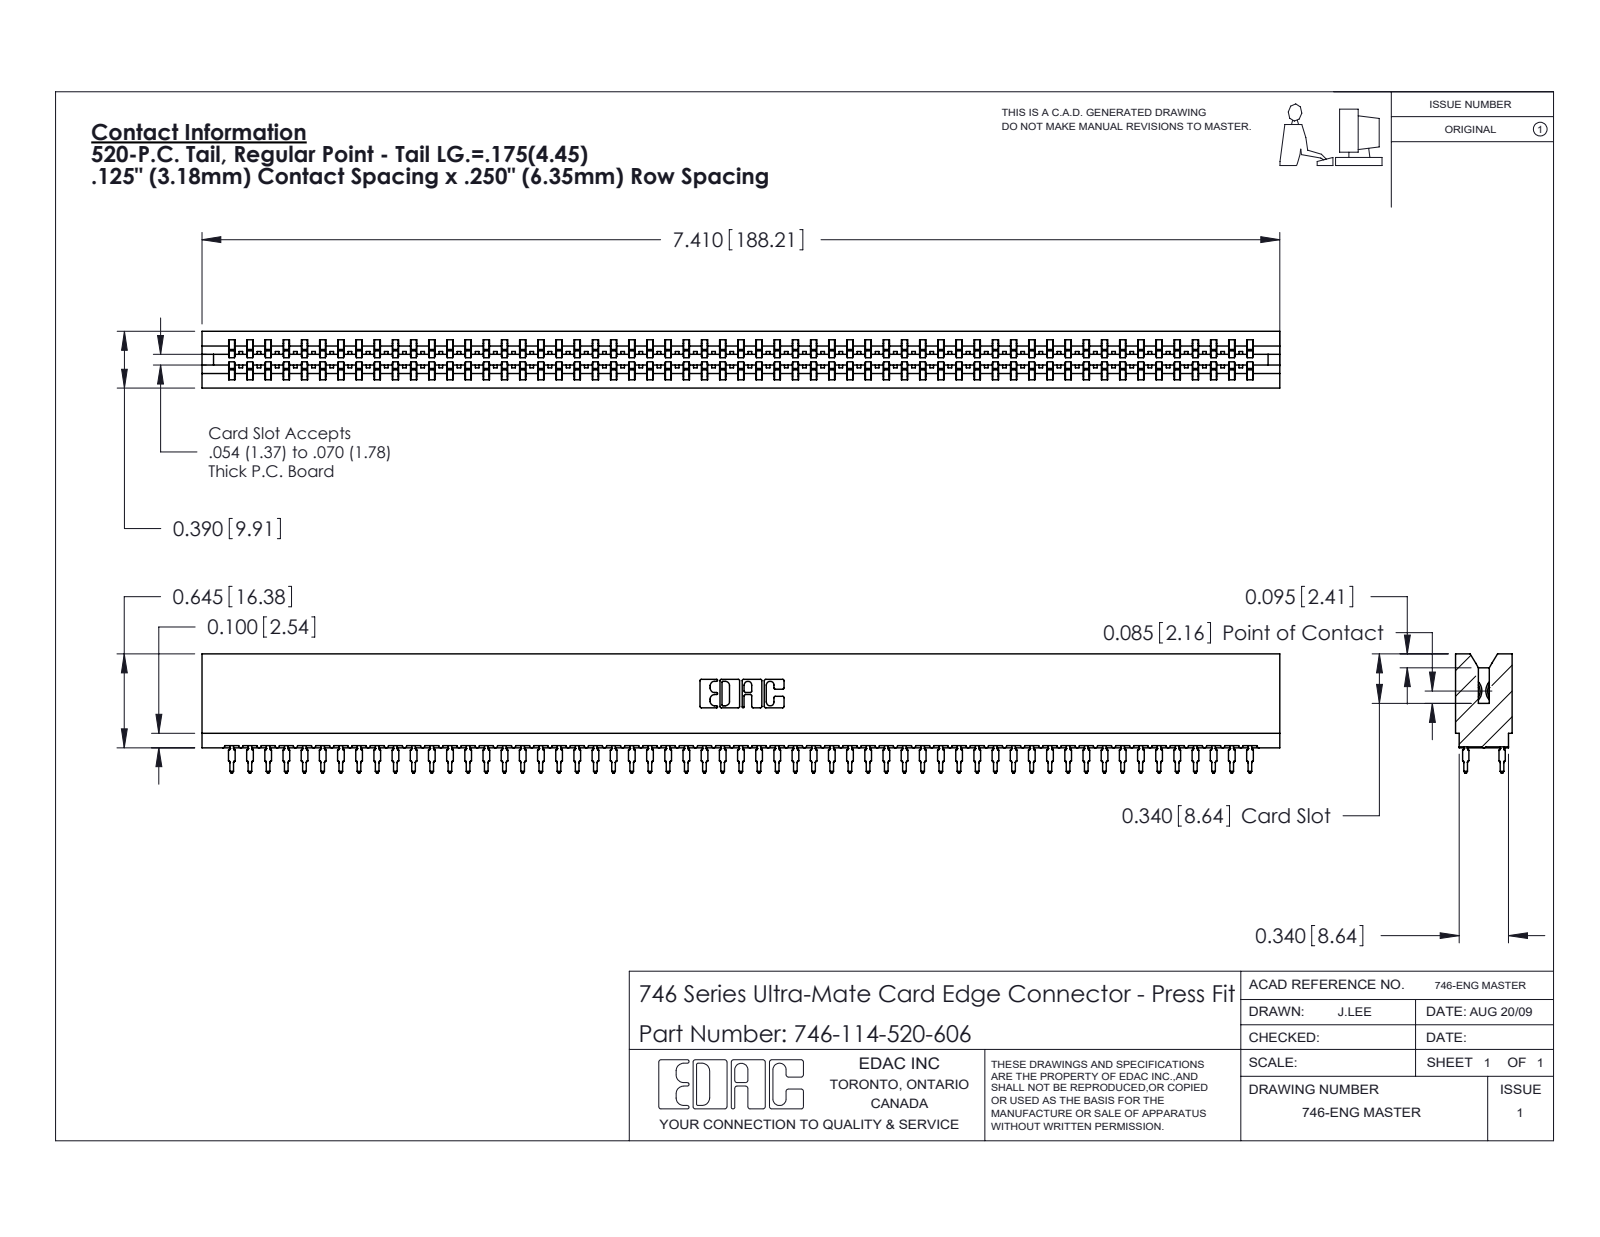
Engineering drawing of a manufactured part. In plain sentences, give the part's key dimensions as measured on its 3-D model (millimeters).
The part is named "746 Part_.340 Slot Depth - 06; 746-114-520-606; 746-292-001_520". Its 3-D file was written by "SolidWorks 2020 (CONFIG_CONTROL_DESIGN)". It is 115 solids with 10301 faces: 5300 planar, 2037 cylindrical and 2964 other. Overall it measures 188.2 by 20.8 by 9.9 millimeters. Its volume is 21 430 cubic millimeters and its surface area 31 170 square millimeters. Partial cylindrical surfaces (rounded edges, fillets, slot ends): 228 of radius 0.5, 58 of radius 0.4, 22 of radius 0.3, 8 of radius 0.1, 8 of radius 0.3, 6 of radius 0.2, 6 of radius 0.8, 3 of radius 0.7. The main face-to-face distances are 1.4, 8.5, 9.9, 0.6, 7.8, 6.4, 7, 2.1, 0.4, 12.7.
